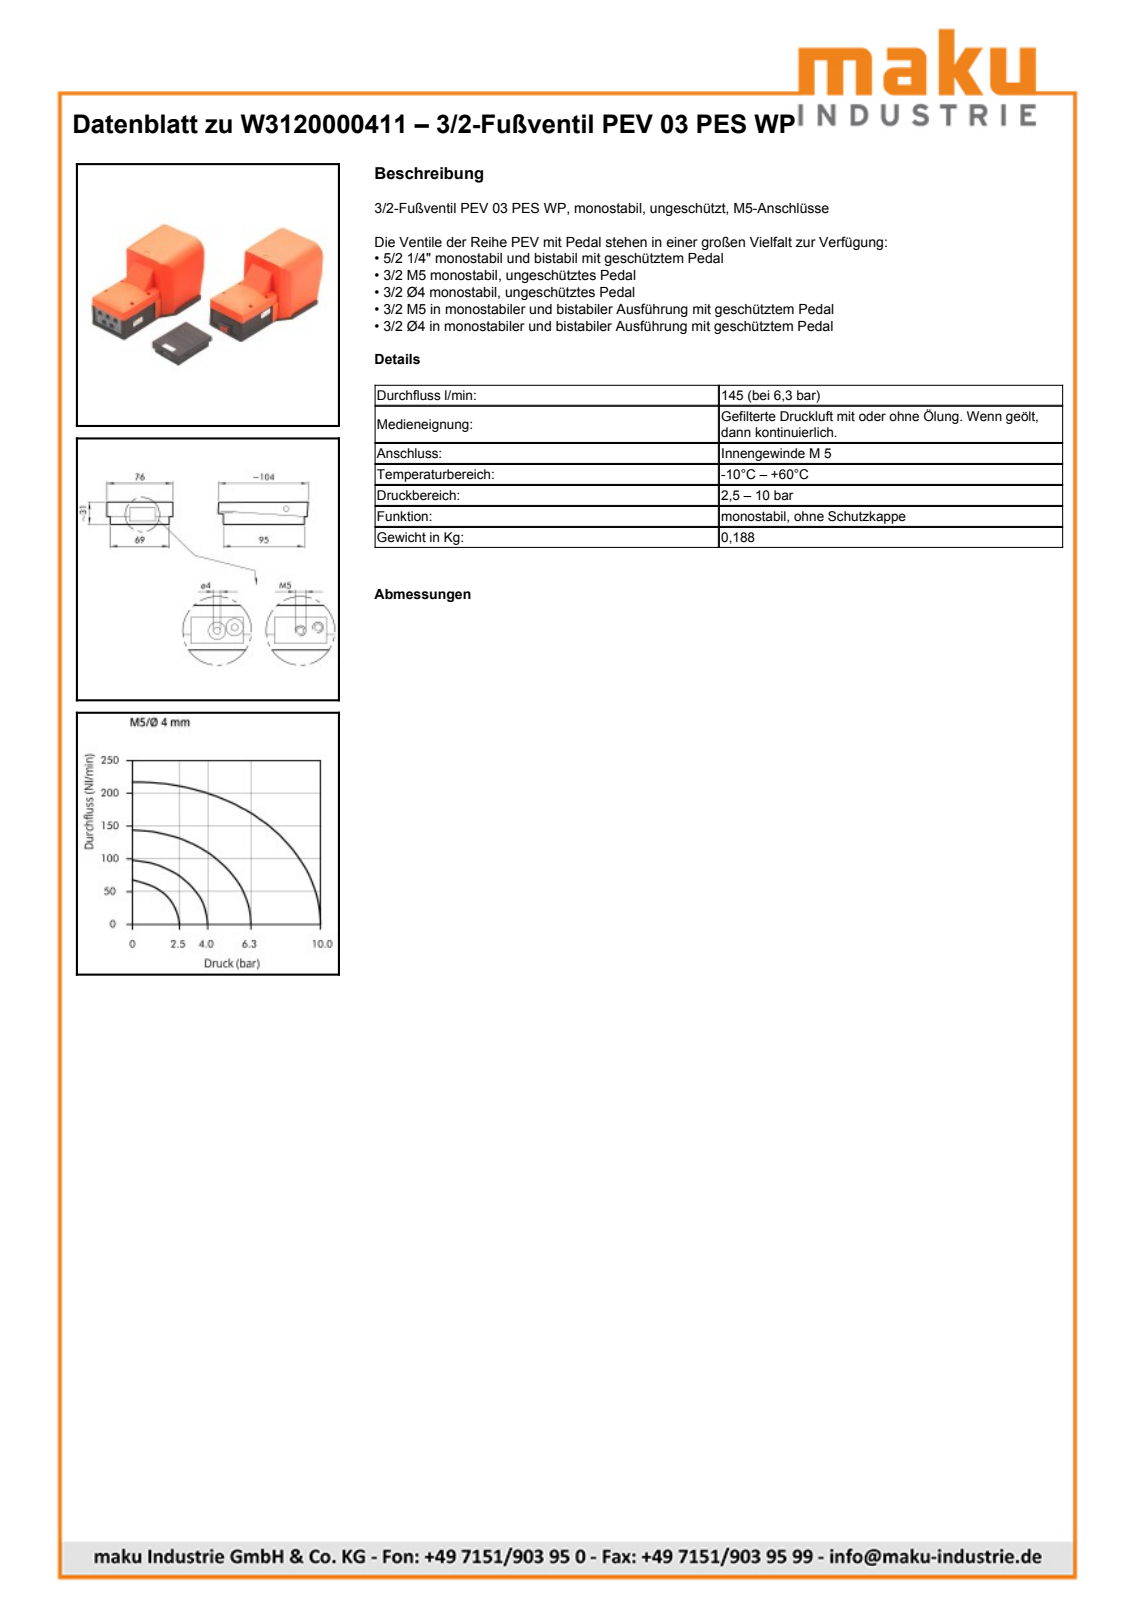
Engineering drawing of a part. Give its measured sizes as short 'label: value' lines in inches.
name: W3120000411(0SWP); W3120000411Pedal; W3120000411Body; W3120000411Body1
written by: PARTsolutions (AUTOMOTIVE_DESIGN)
unit: in
bodies: 3 solids, 217 faces (131 planar, 79 cylindrical, 7 other)
size: 4.094 × 3.031 × 1.22
volume: 4.933 in³; area: 91.12 in²
holes: 2× ⌀0.094, 2× ⌀0.163, 2× ⌀0.177, 1× ⌀0.236
bosses: 1× ⌀0.394, 1× ⌀0.165
rounds: 30× R0.039, 6× R0.079, 1× R0.169
face distances: 0.098, 1.094, 0.138, 0.768, 0.669, 0.079, 2.756, 1.016, 0.236, 1.193
hole spacings: 0.368, 0.187, 0.41, 0.425, 0.735, 0.756
